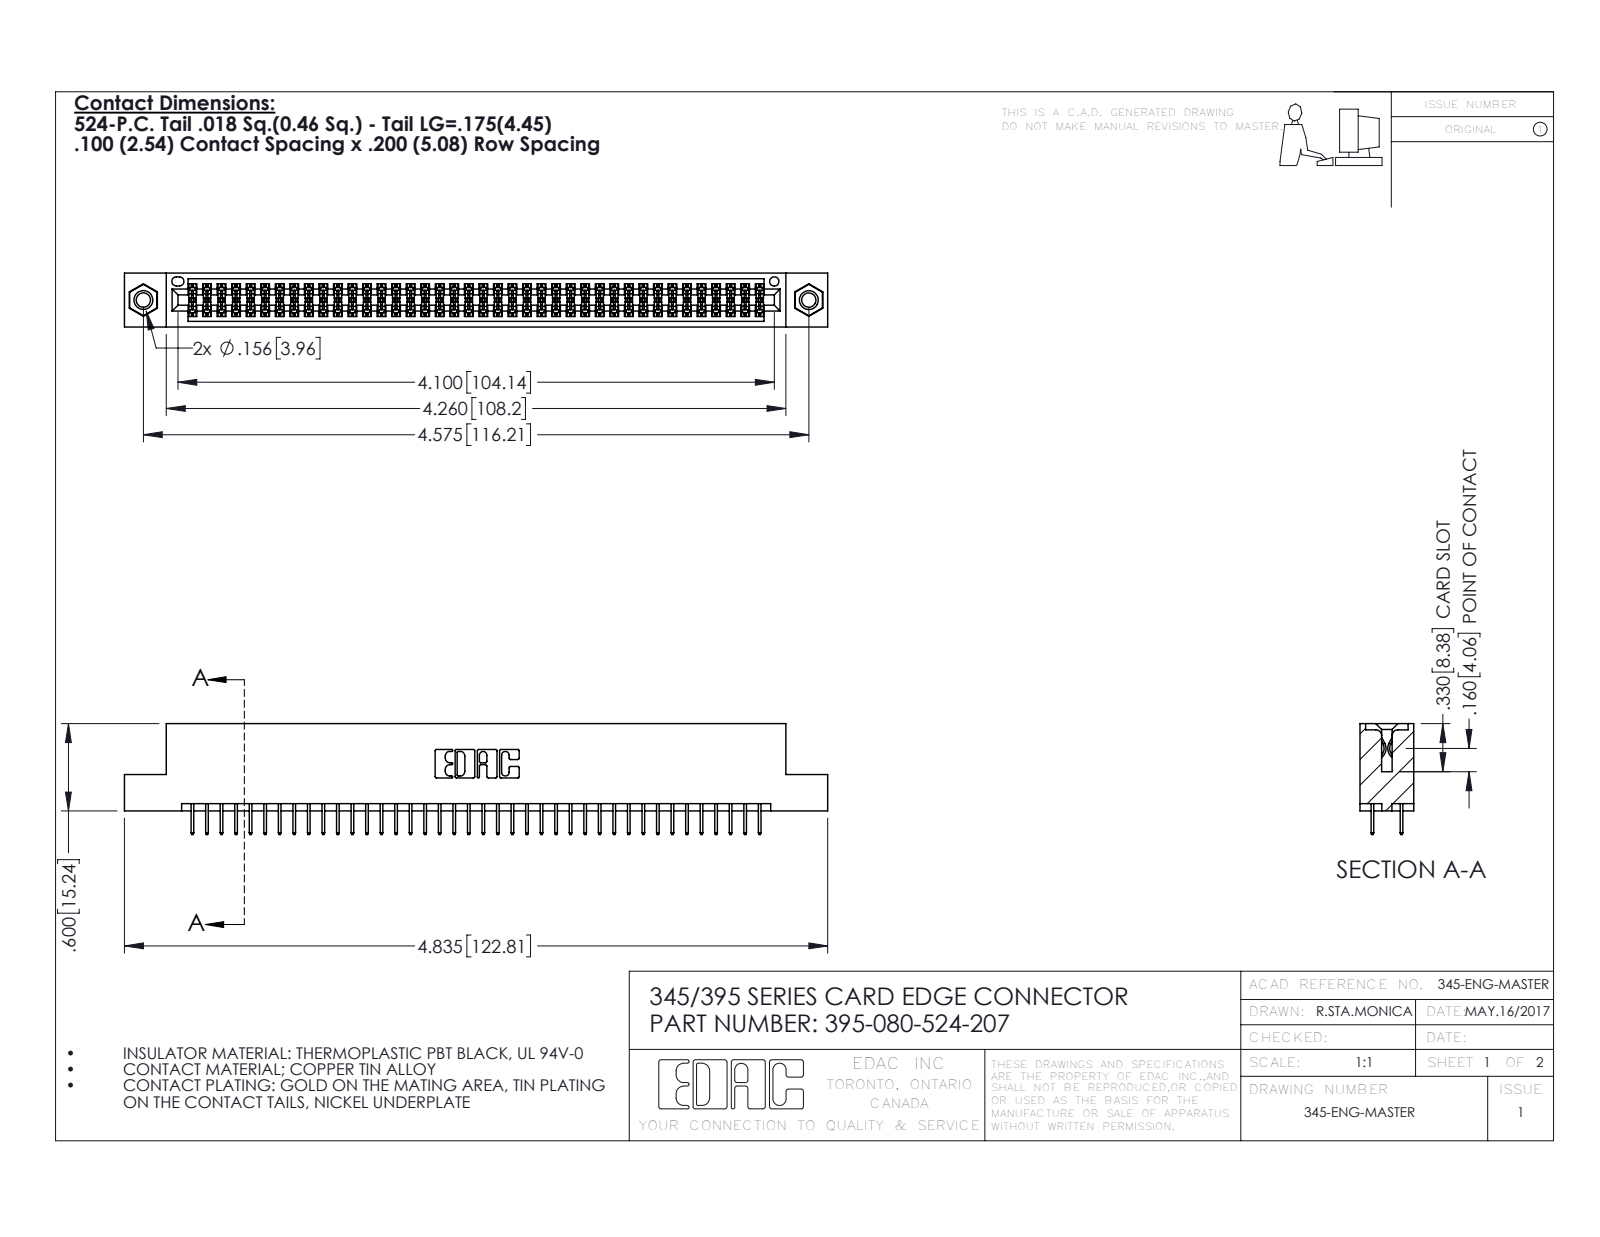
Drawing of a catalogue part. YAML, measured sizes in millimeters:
part_name: "395-080-524-207; 345 Part_Flush Mounting Lugs - 0.156 Dia-TI; 345-292-001_345-293-124; 345-250-001_345-250-005-103"
step_written_by: "SolidWorks 2016 (CONFIG_CONTROL_DESIGN)"
units: millimeters
bodies: {solids: 83, faces: 4506, planar: 3232, cylindrical: 1258, other: 16}
overall_size: [122.8, 19.4, 9.4]
volume: 11800
surface_area: 17080
round_holes:
  - {diameter: 2.5, count: 2}
  - {diameter: 3.2, count: 2}
  - {diameter: 4, count: 2}
  - {diameter: 1.6, count: 1}
round_bosses_or_shafts:
  - {diameter: 3.9, count: 2}
partial_cylinders:
  - {radius: 0.2, count: 120}
  - {radius: 0.3, count: 22}
  - {radius: 0.2, count: 6}
  - {radius: 0.8, count: 6}
  - {radius: 0.7, count: 3}
  - {radius: 0.4, count: 2}
  - {radius: 0.5, count: 2}
  - {radius: 0.6, count: 2}
face_to_face_distances: [1.8, 7.6, 5.1, 9.4, 2.5, 6.9, 0.6, 5.7, 1.8, 4.4]
hole_center_spacings: [6.9, 110.2, 116.2]
